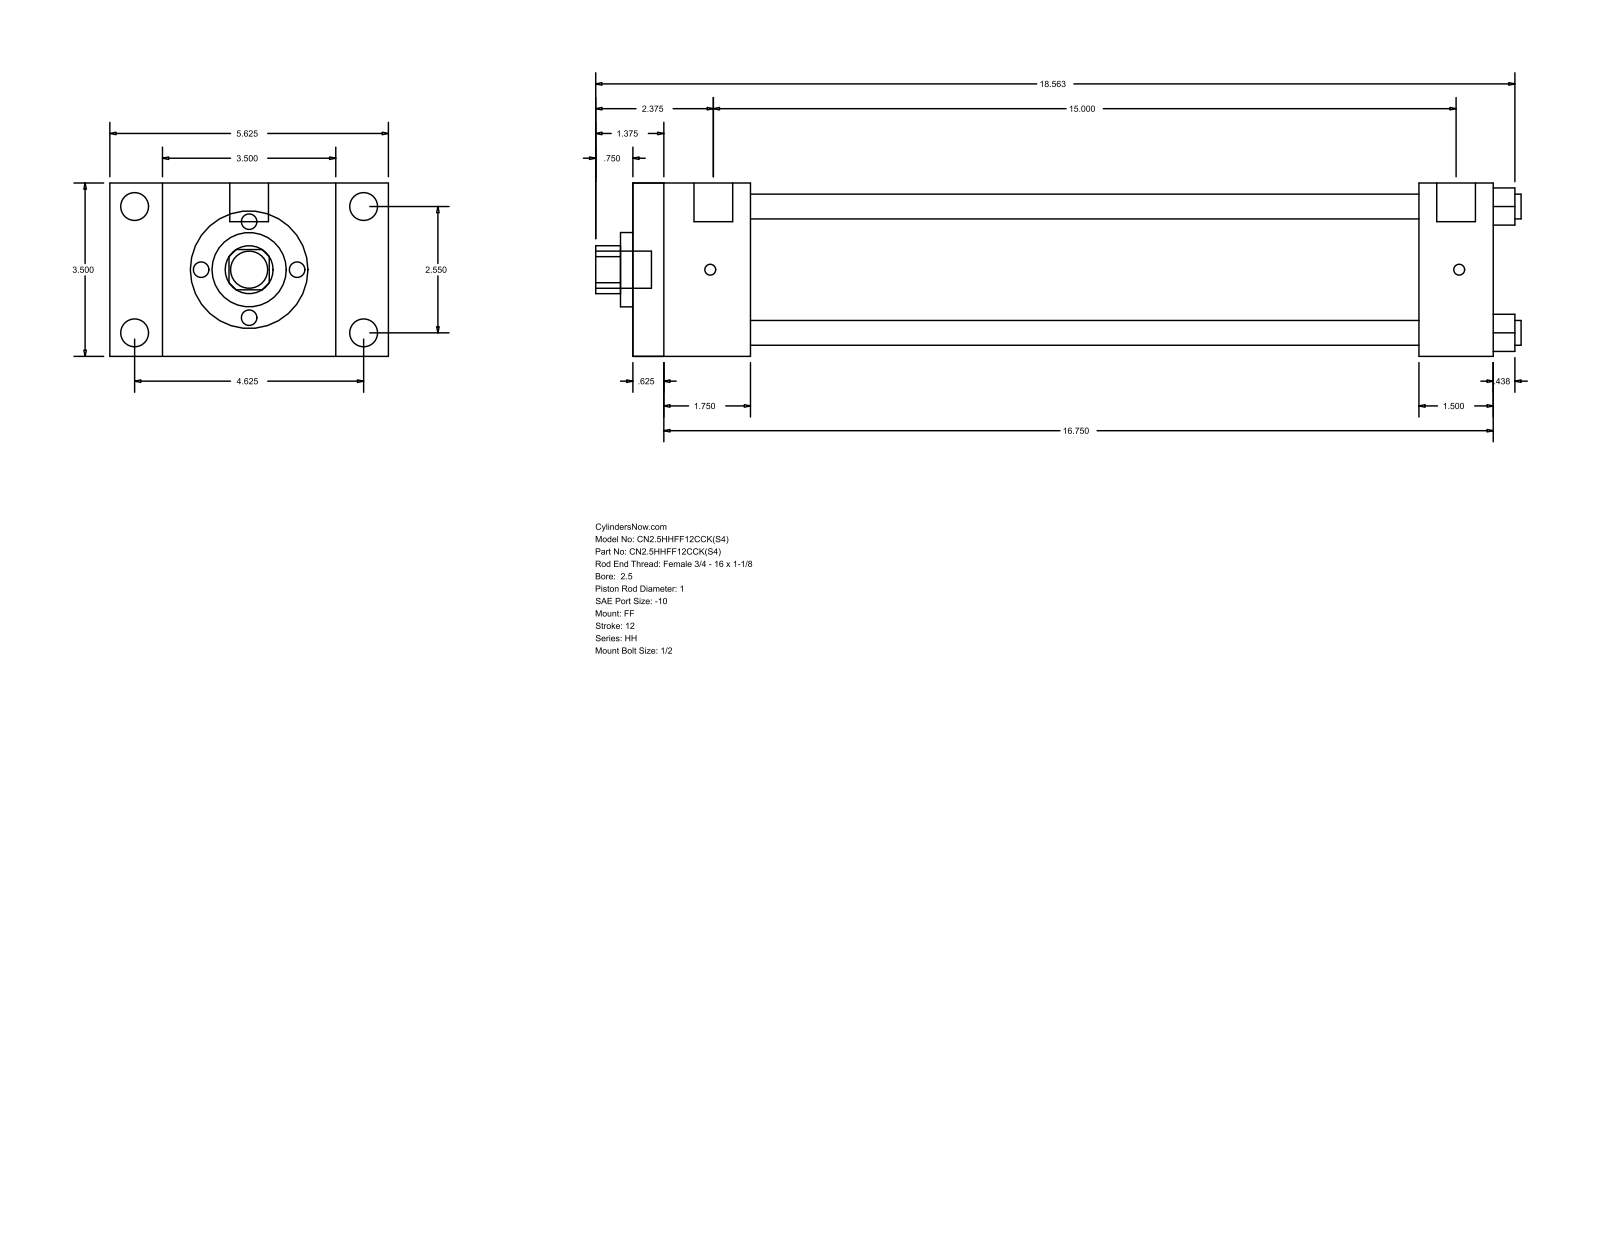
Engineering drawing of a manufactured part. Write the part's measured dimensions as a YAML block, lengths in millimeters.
part_name: "HH_FF__0250_1"
step_written_by: "GSSL Pune (CONFIG_CONTROL_DESIGN)"
units: millimeters
bodies: {solids: 0, faces: 92, planar: 64, cylindrical: 28, other: 0}
overall_size: [474.66, 142.88, 88.9]
round_holes:
  - {diameter: 12.7, count: 4}
  - {diameter: 25.4, count: 1}
  - {diameter: 38.1, count: 1}
  - {diameter: 73.03, count: 1}
round_bosses_or_shafts:
  - {diameter: 14.3, count: 4}
  - {diameter: 5.56, count: 4}
  - {diameter: 19.84, count: 2}
  - {diameter: 19.05, count: 1}
partial_cylinders:
  - {radius: 12.29, count: 1}
face_to_face_distances: [88.9, 441.33, 15.87, 425.46, 60.33, 44.46, 381, 403.22, 387.35, 342.89]
hole_center_spacings: [45.79, 64.76, 91.58]
